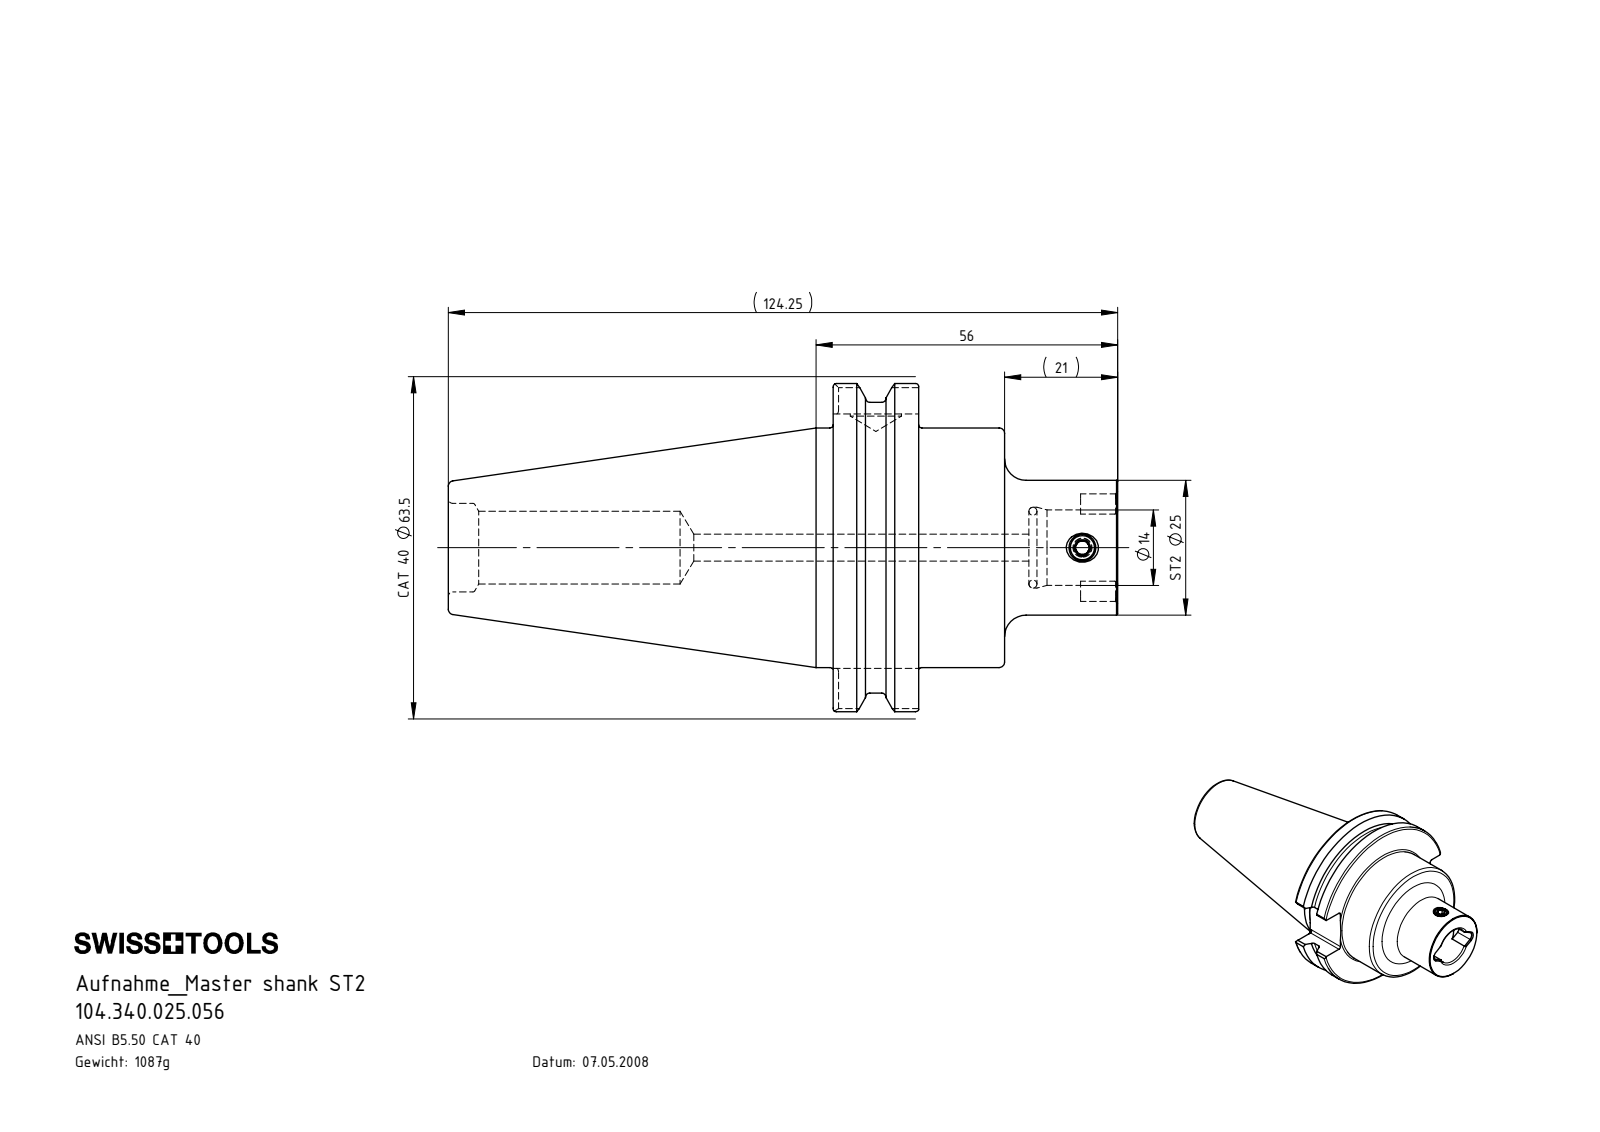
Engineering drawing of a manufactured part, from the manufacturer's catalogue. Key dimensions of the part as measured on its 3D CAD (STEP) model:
Part name (STEP PRODUCT): DIN 3771 - 12x1.5; CT4.ST2.K01.056; CT4-ST2.K01.056_B; ST2-ER1.001.006_A
STEP written by: SolidWorks 2017 (AUTOMOTIVE_DESIGN)
Units: millimetres
Bodies: 3 solids, 116 faces (50 planar, 28 cylindrical, 38 other)
Overall size (bounding box): 124.25 × 63.5 × 60.87
Volume: 138 489 mm³ · Surface area: 24 155 mm²
Round holes (diameter × count): ⌀2.5 ×1, ⌀4.5 ×1, ⌀5 ×1, ⌀9.5 ×1, ⌀13.5 ×1, ⌀14 ×1, ⌀15 ×1, ⌀16.43 ×1
Round bosses / shafts (diameter × count): ⌀63.5 ×1, ⌀56.36 ×1, ⌀44.45 ×1, ⌀25 ×1, ⌀5 ×1
Partial cylindrical surfaces — rounded edges, fillets, slot ends (radius × count): R0.8 ×8, R1.8 ×2
Main face-to-face distances: 15.87, 31.82, 15.95, 52.82, 36.95, 21, 47.2, 71.43, 87.3, 103.25
